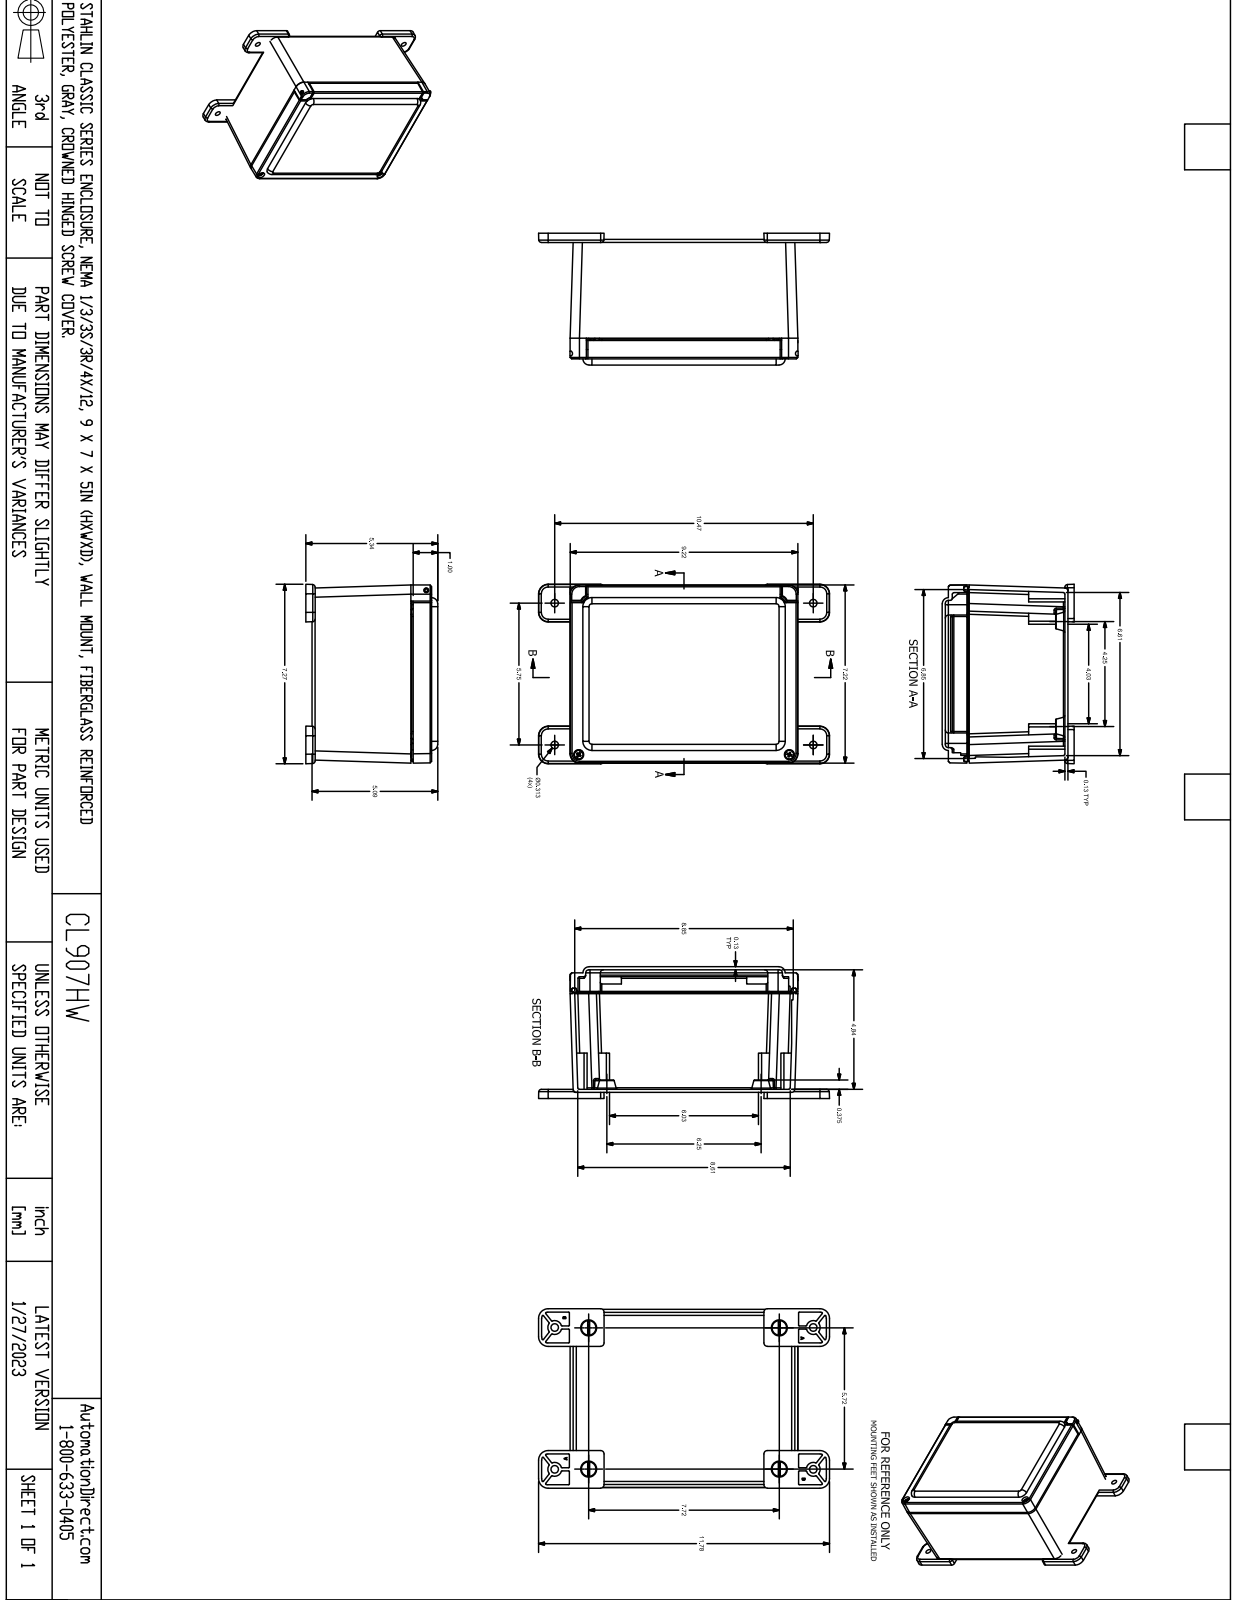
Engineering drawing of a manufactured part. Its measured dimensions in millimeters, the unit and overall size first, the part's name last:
Units: millimetres
Overall size (bounding box): 299.3 × 184.7 × 135.7
Round holes (diameter × count): ⌀4 ×6, ⌀7.1 ×6, ⌀8 ×4, ⌀8 ×4, ⌀8.7 ×4, ⌀13.5 ×4, ⌀2.4 ×2, ⌀4 ×2, ⌀4.8 ×2, ⌀5.6 ×2, ⌀5.8 ×2, ⌀7.1 ×2
Round bosses / shafts (diameter × count): ⌀6.9 ×6, ⌀5.8 ×4, ⌀9.5 ×2, ⌀9.5 ×2, ⌀3.5 ×2, ⌀8.3 ×1, ⌀4.6 ×1, ⌀3.2 ×1
Partial cylindrical surfaces — rounded edges, fillets, slot ends (radius × count): R0.8 ×58, R0.8 ×56, R3.2 ×42, R1.6 ×19, R6.4 ×16, R2.5 ×12, R1.6 ×11, R9.5 ×10
Main face-to-face distances: 3.2, 126.2, 4.7, 129.4, 123, 6.4, 4.7, 3.2, 132.6, 19.1
Hole centre spacings: 56.8, 137.8, 155.9, 169.2, 213.2, 247.4, 26.4, 41
Volume: 1 009 000 mm³ · Surface area: 452 100 mm²
Bodies: 29 solids, 1467 faces (641 planar, 414 cylindrical, 412 other)
Part name (STEP PRODUCT): CE907HW
STEP written by: SolidWorks 2018 (AUTOMOTIVE_DESIGN)
